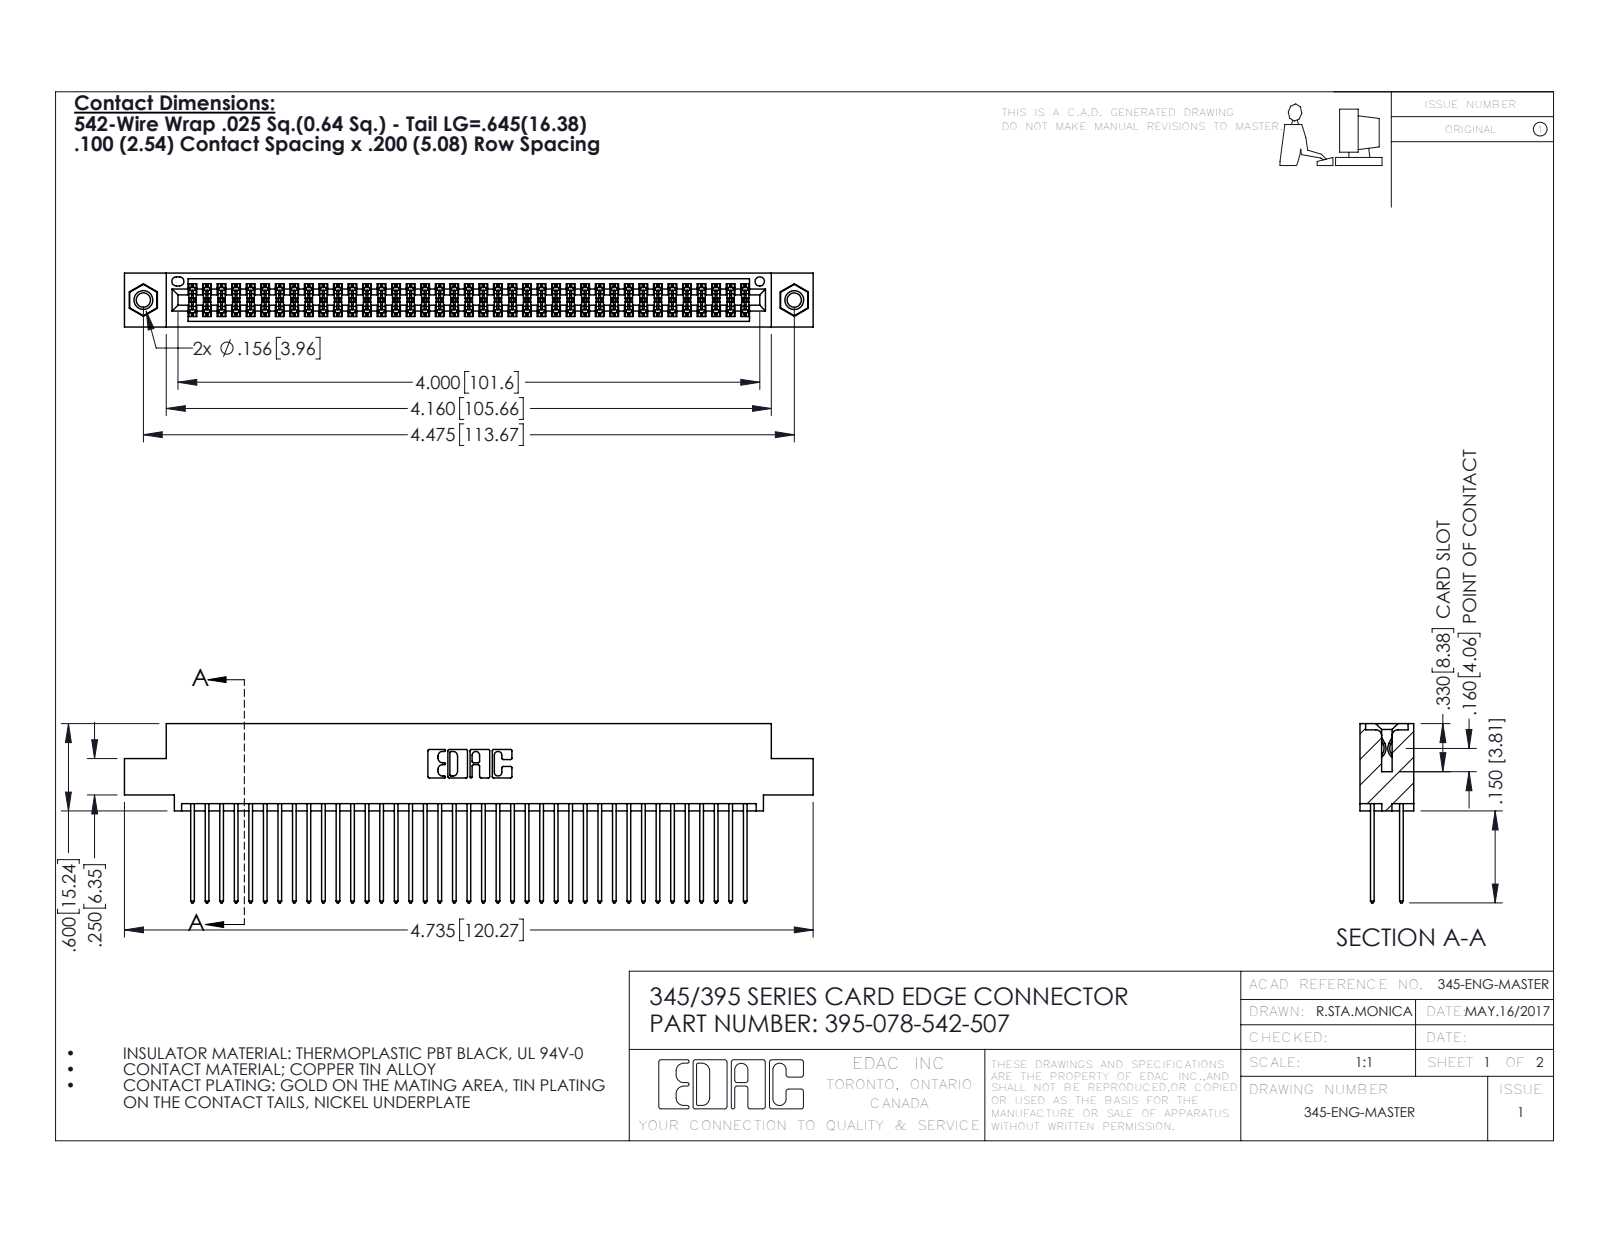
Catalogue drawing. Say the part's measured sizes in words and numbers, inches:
The part is named "395-078-542-507; 345-292-001_345-293-142; 345 Part_0.110 Offset - 0.156 Dia-TI; 345-250-001_345-250-005-103". Its 3-D file was written by "SolidWorks 2016 (CONFIG_CONTROL_DESIGN)". It is 81 solids with 4090 faces: 2690 planar, 1384 cylindrical and 16 other. Overall it measures 4.735 by 1.232 by 0.37 inches. Its volume is 0.728 cubic inches and its surface area 30.07 square inches. Round holes: 2 of diameter 0.098, 2 of diameter 0.125, 2 of diameter 0.156, 1 of diameter 0.064. Round bosses or shafts: 2 of diameter 0.155. Partial cylindrical surfaces (rounded edges, fillets, slot ends): 117 of radius 0.006, 78 of radius 0.01, 22 of radius 0.01, 6 of radius 0.007, 6 of radius 0.031, 3 of radius 0.026, 2 of radius 0.014, 2 of radius 0.019. The main face-to-face distances are 0.072, 0.298, 0.2, 0.098, 0.272, 0.025, 0.225, 0.37, 0.175, 0.149. The hole center spacings are 0.27, 4.239, 4.475.
